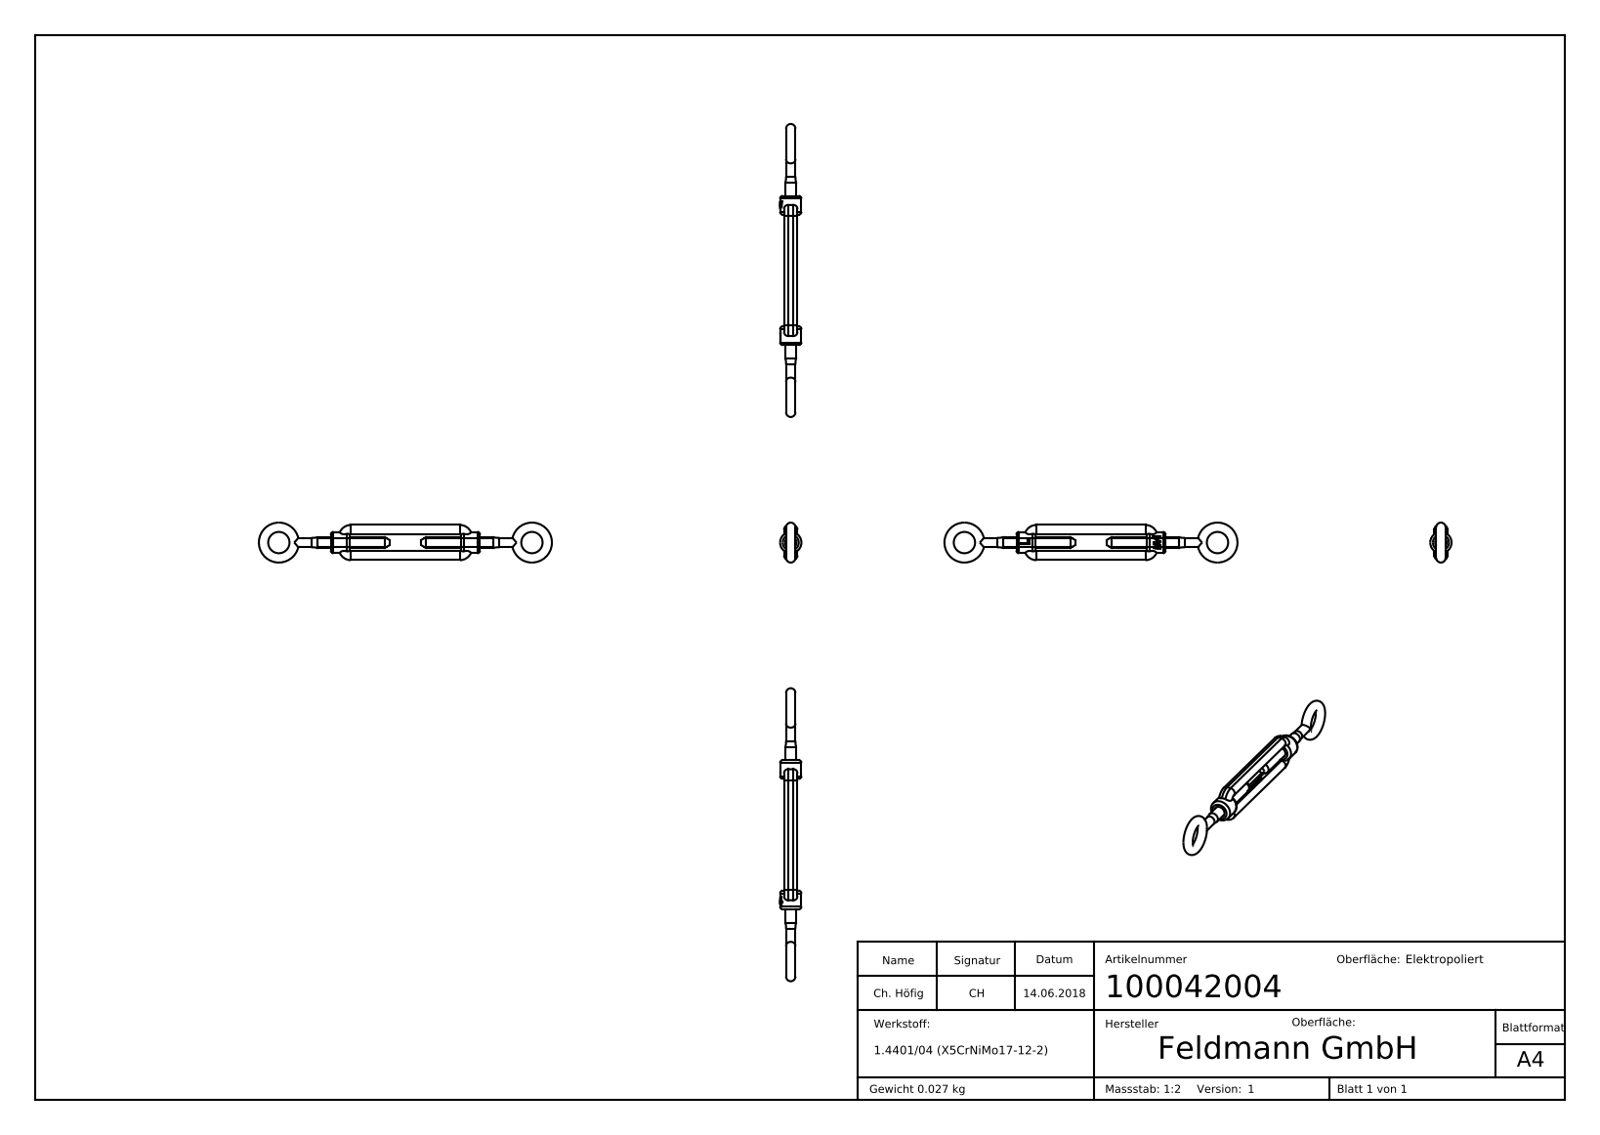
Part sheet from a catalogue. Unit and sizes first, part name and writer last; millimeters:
Units: millimetres
Overall size (bounding box): 110 × 15 × 8
Round holes (diameter × count): ⌀3.3 ×1
Round bosses / shafts (diameter × count): ⌀8 ×1, ⌀4 ×1, ⌀3.5 ×1
Partial cylindrical surfaces — rounded edges, fillets, slot ends (radius × count): R1 ×4, R1.75 ×4, R4.5 ×4, R3.98 ×1
Main face-to-face distances: 9.7, 3.5, 13.2, 6.2, 7, 49, 56, 42, 22, 34
Volume: 3 431 mm³ · Surface area: 3 477 mm²
Bodies: 3 solids, 335 faces (152 planar, 32 cylindrical, 151 other)
Part name (STEP PRODUCT): 10004200X Teil1_100042004 Teil1; 10004200X Teil2_100042004 Teil2; 100042004; 10004200X Teil3_100042004 Teil3
STEP written by: SolidWorks 2015 (CONFIG_CONTROL_DESIGN)
